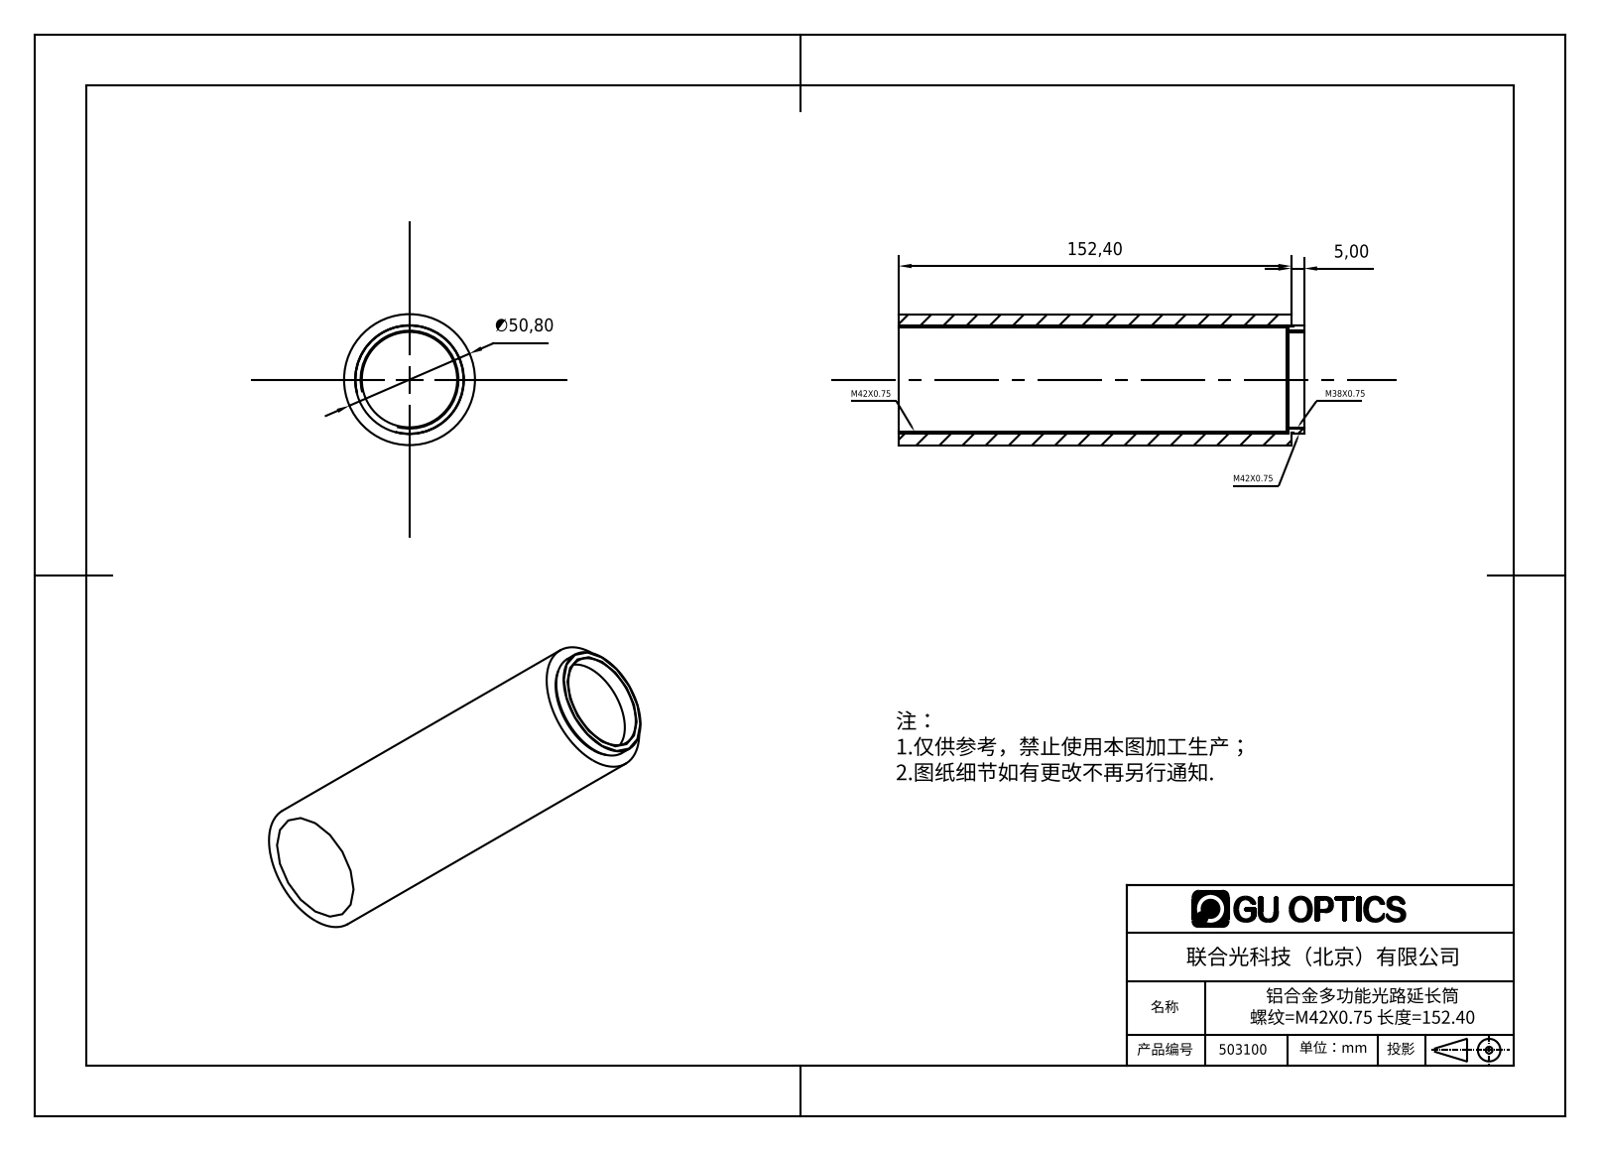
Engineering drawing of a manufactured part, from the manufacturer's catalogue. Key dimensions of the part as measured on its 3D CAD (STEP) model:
Part name (STEP PRODUCT): 503100
STEP written by: SolidWorks 2016 (AUTOMOTIVE_DESIGN)
Units: millimetres
Bodies: 1 solid, 18 faces (6 planar, 12 cylindrical, 0 other)
Overall size (bounding box): 157.4 × 50.8 × 50.8
Volume: 117 061 mm³ · Surface area: 47 124 mm²
Round holes (diameter × count): ⌀37 ×1, ⌀40.2 ×1, ⌀42.2 ×1
Round bosses / shafts (diameter × count): ⌀50.8 ×1, ⌀41 ×1
Main face-to-face distances: 152.4, 1, 157.4, 5, 151.4, 6, 2, 150.4, 7, 153.4
